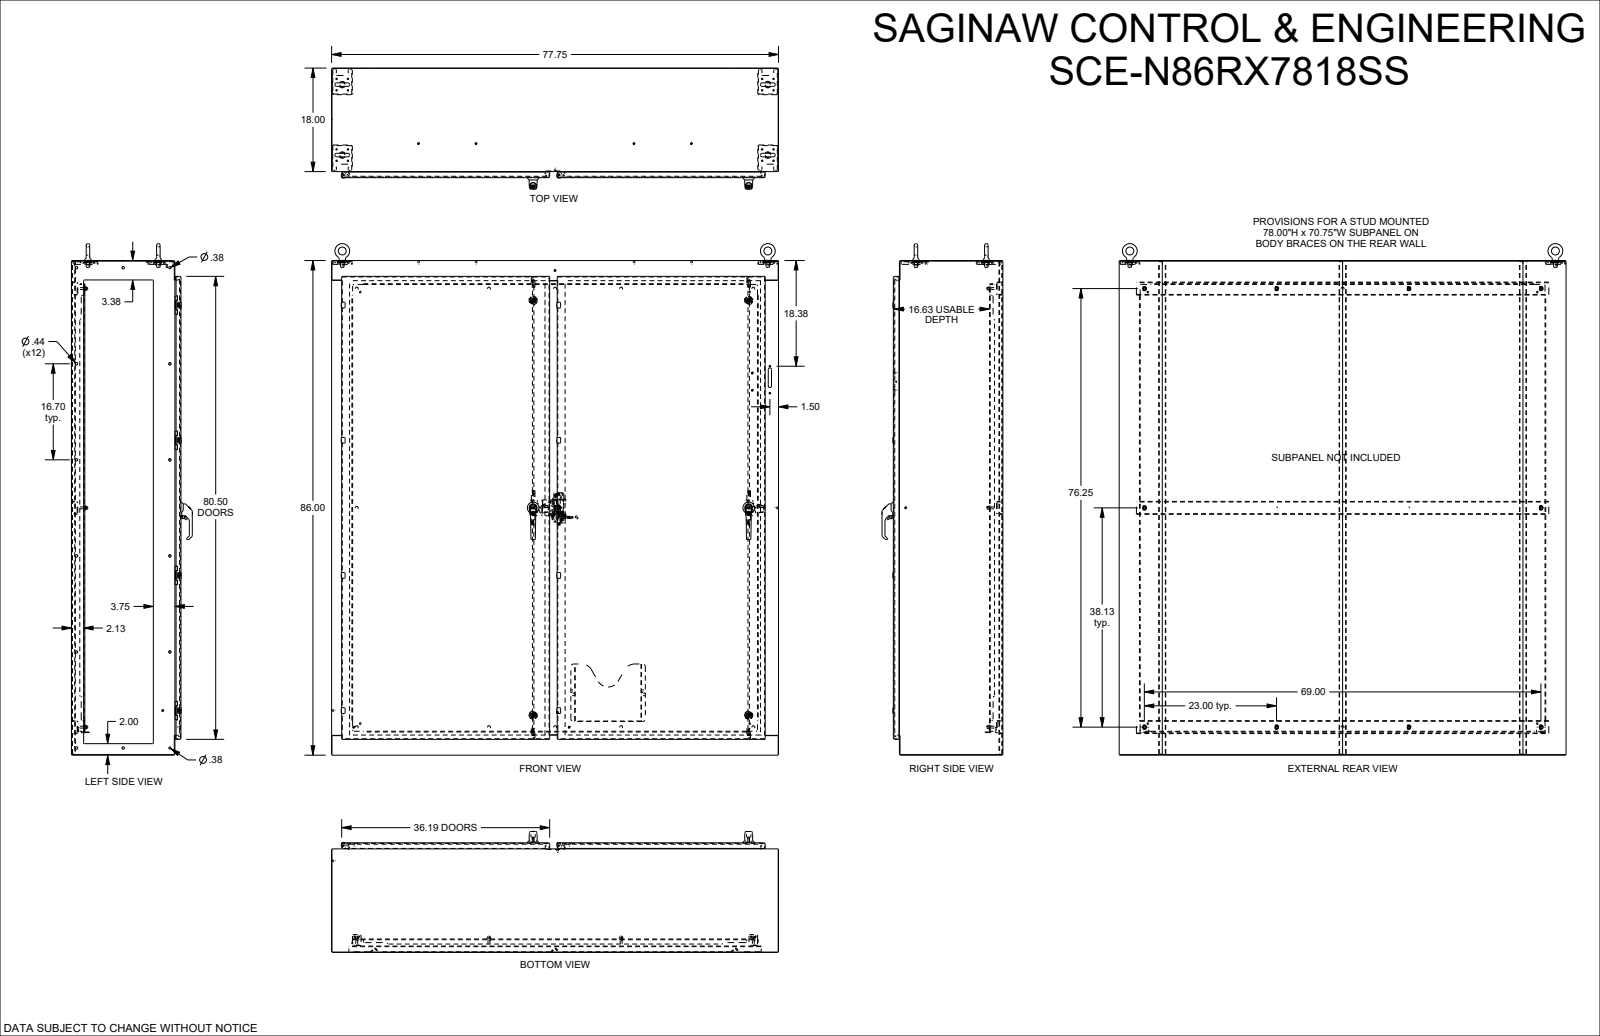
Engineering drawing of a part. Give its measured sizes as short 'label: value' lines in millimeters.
name: SCE-N86RX7818
written by: SolidWorks 2023 (AUTOMOTIVE_DESIGN)
unit: mm
bodies: 89 solids, 9556 faces (3823 planar, 3171 cylindrical, 2562 other)
size: 2260 × 1974.9 × 534.6
volume: 36 690 000 mm³; area: 27 490 000 mm²
holes: 24× ⌀6.4, 18× ⌀9.5, 16× ⌀5.2, 16× ⌀6.2, 10× ⌀11.1, 8× ⌀1, 8× ⌀4.3, 8× ⌀5.5, 4× ⌀5.1, 4× ⌀6.5, 4× ⌀8.7, 4× ⌀8.7
bosses: 24× ⌀4.3, 19× ⌀6.4, 16× ⌀6.1, 15× ⌀6.3, 10× ⌀5, 4× ⌀35.6, 4× ⌀32.2, 4× ⌀29.8
rounds: 233× R0.8, 166× R0.4, 144× R4.2, 144× R5, 96× R3.2, 59× R1, 57× R0.5, 48× R0.5
face distances: 2.6, 481.4, 478.8, 484.1, 2181.8, 454.6, 26.9, 451.9, 29.5, 2184.4
hole spacings: 596.9, 424.2, 591.8, 50.3, 848.4, 943.4, 952.5, 35.6
